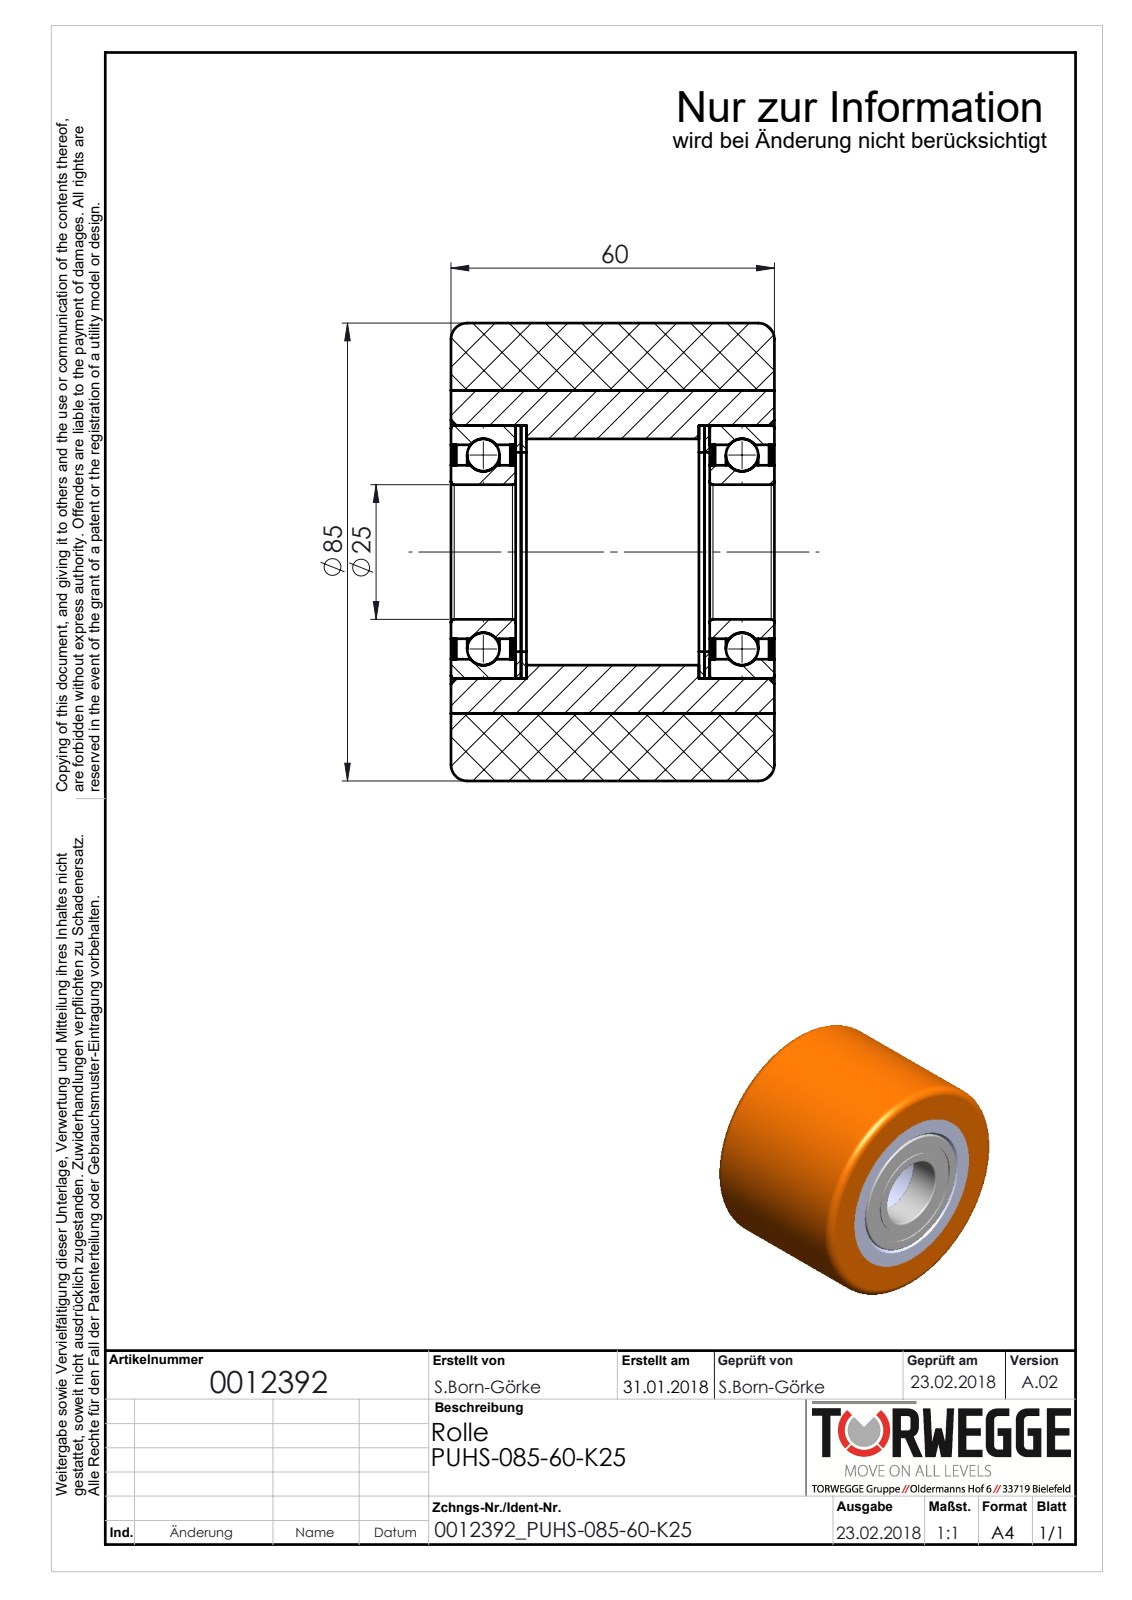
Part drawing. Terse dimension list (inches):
name: 0012392_PUHS-085-60-K25
written by: SolidWorks 2016 (AUTOMOTIVE_DESIGN)
unit: in
bodies: 16 solids, 158 faces (30 planar, 68 cylindrical, 60 other)
size: 3.346 × 3.346 × 2.362
volume: 16.71 in³; area: 129.1 in²
holes: 1× ⌀0.984, 1× ⌀1.268, 1× ⌀1.457, 1× ⌀1.567, 1× ⌀1.654, 1× ⌀2.362
bosses: 1× ⌀3.346, 1× ⌀1.85
face distances: 0.039, 1.89, 2.362, 0.472, 0.02, 0.512, 1.85, 1.378, 1.339, 1.811
